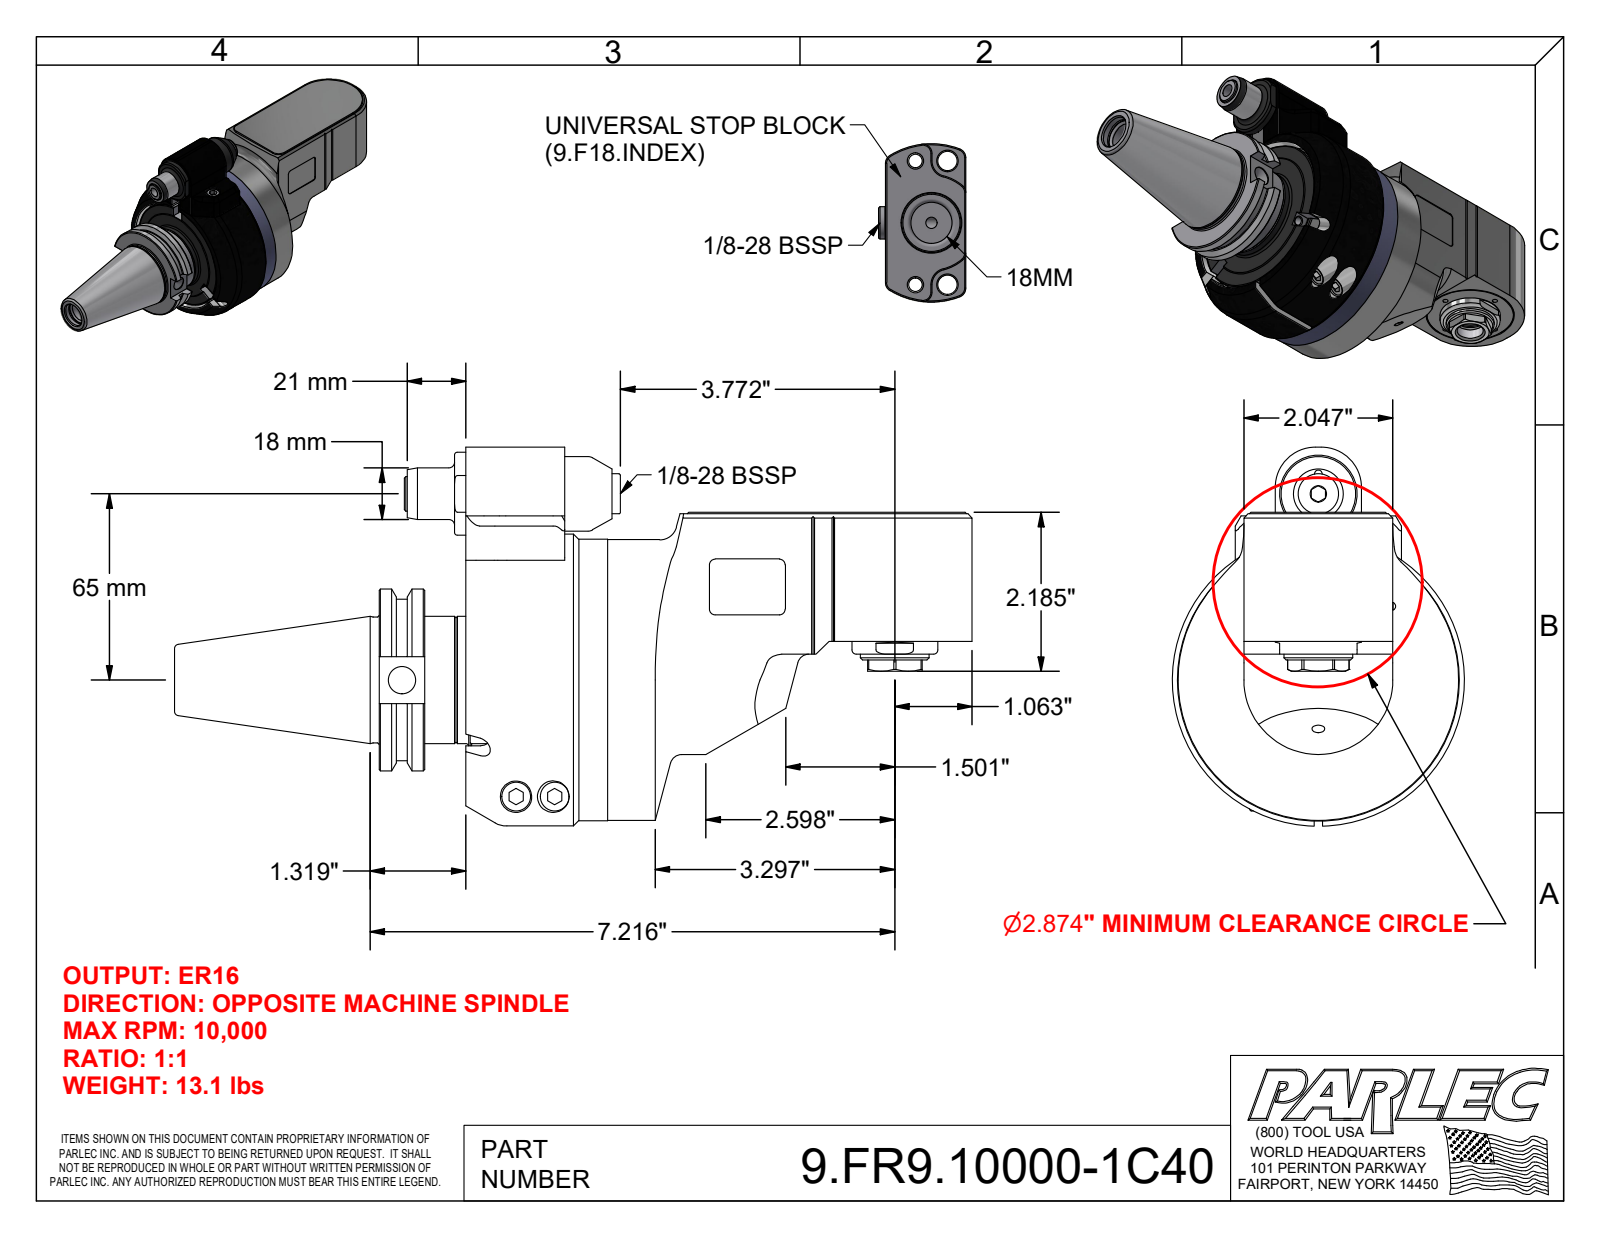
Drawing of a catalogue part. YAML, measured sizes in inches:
part_name: "9.FR9.10000-1C40; 9.FR9.10000; 9_GA1_446_2_1_C40; 9FL1ATC (+4 more)"
step_written_by: "Autodesk Inventor 2022 (AUTOMOTIVE_DESIGN)"
units: inches
bodies: {solids: 5, faces: 570, planar: 242, cylindrical: 161, other: 167}
overall_size: [10.966, 5.206, 4.016]
volume: 59.23
surface_area: 244.8
round_holes:
  - {diameter: 0.335, count: 22}
  - {diameter: 0.102, count: 10}
  - {diameter: 0.197, count: 7}
  - {diameter: 0.118, count: 3}
  - {diameter: 0.433, count: 3}
  - {diameter: 0.165, count: 2}
  - {diameter: 0.409, count: 2}
  - {diameter: 0.512, count: 2}
  - {diameter: 0.098, count: 1}
  - {diameter: 0.13, count: 1}
  - {diameter: 0.177, count: 1}
  - {diameter: 0.256, count: 1}
round_bosses_or_shafts:
  - {diameter: 0.394, count: 4}
  - {diameter: 0.236, count: 4}
  - {diameter: 0.315, count: 2}
  - {diameter: 0.098, count: 2}
  - {diameter: 4.016, count: 1}
  - {diameter: 3.874, count: 1}
  - {diameter: 3.858, count: 1}
  - {diameter: 3.031, count: 1}
partial_cylinders:
  - {radius: 0.079, count: 12}
  - {radius: 0.157, count: 4}
  - {radius: 0.02, count: 2}
  - {radius: 0.039, count: 2}
  - {radius: 0.138, count: 2}
  - {radius: 0.197, count: 2}
  - {radius: 0.551, count: 2}
  - {radius: 0.984, count: 2}
face_to_face_distances: [0.02, 0.659, 2.047, 1.22, 0.276, 1.22, 0.335, 1.555, 0.197, 1.083]
hole_center_spacings: [1.496, 2.992, 0.339, 0.365, 0.382, 0.433, 0.435, 0.689]
